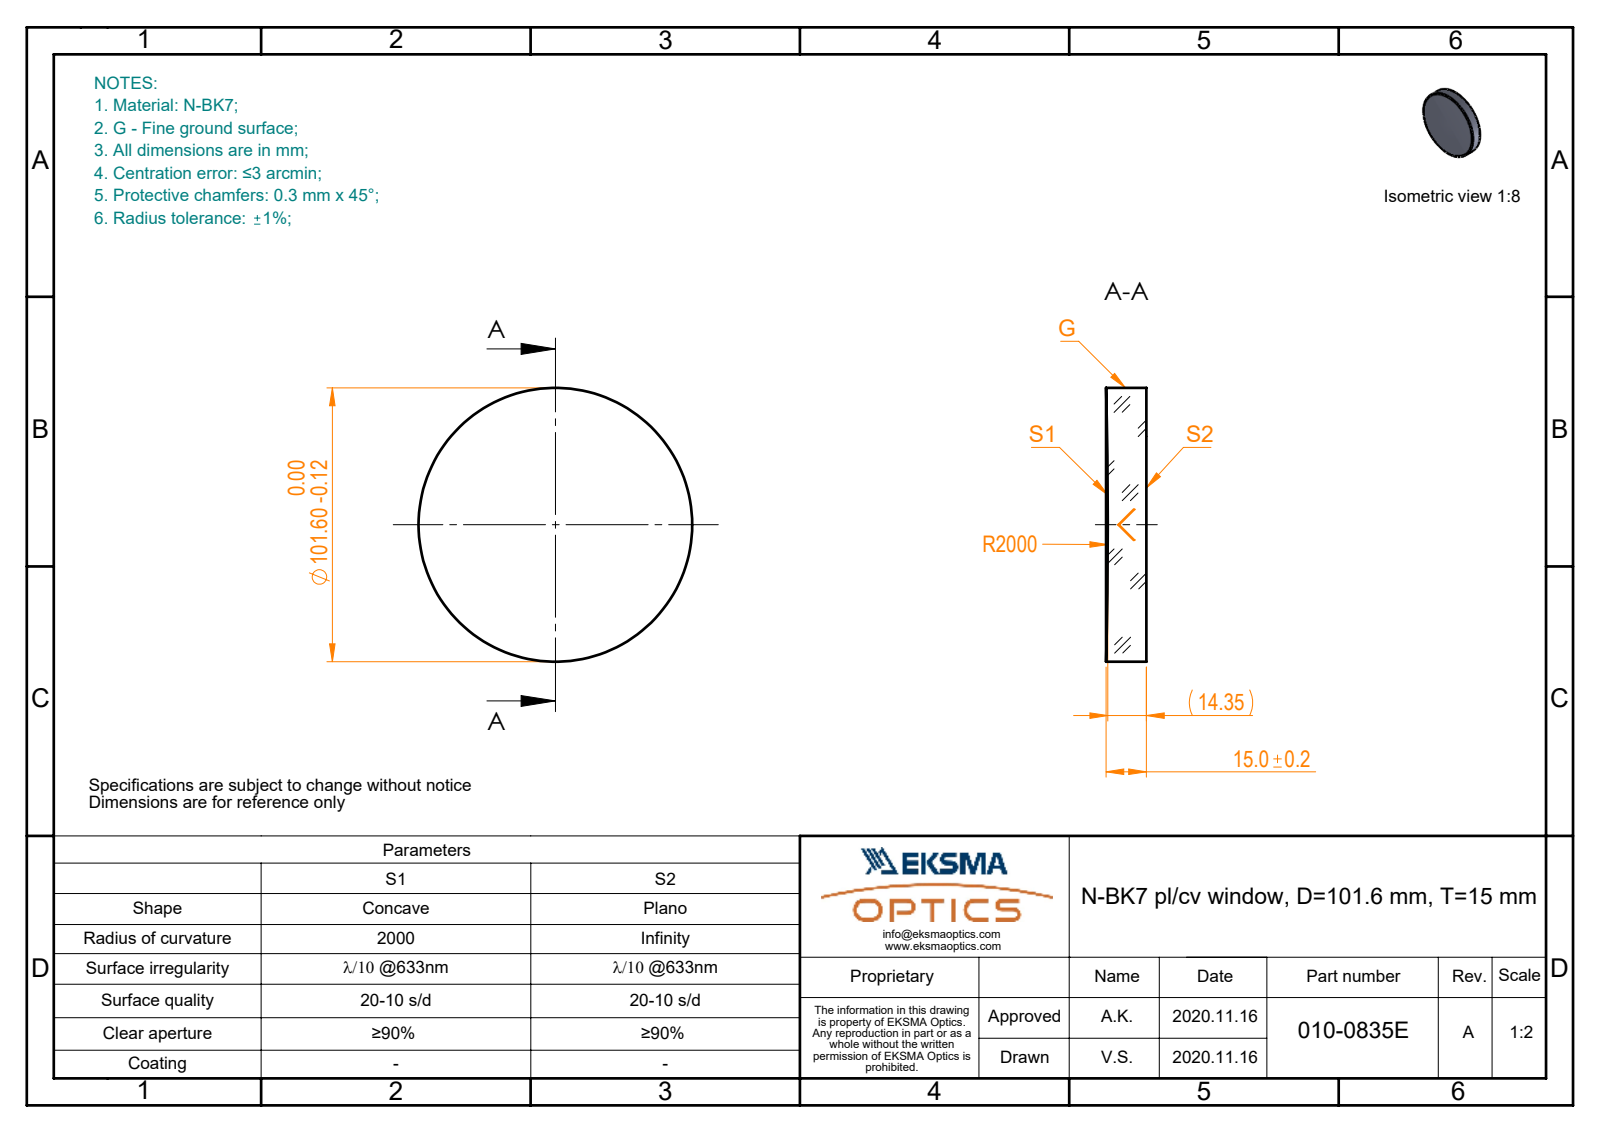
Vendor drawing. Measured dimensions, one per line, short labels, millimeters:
name: 010-0835E_N-BK7_PCV_window
written by: SolidWorks 2019 (CONFIG_CONTROL_DESIGN)
unit: mm
bodies: 1 solid, 5 faces (1 planar, 2 cylindrical, 2 other)
size: 101.6 × 101.6 × 15
volume: 118 994 mm³; area: 21 004 mm²
bosses: 1× ⌀101.6
